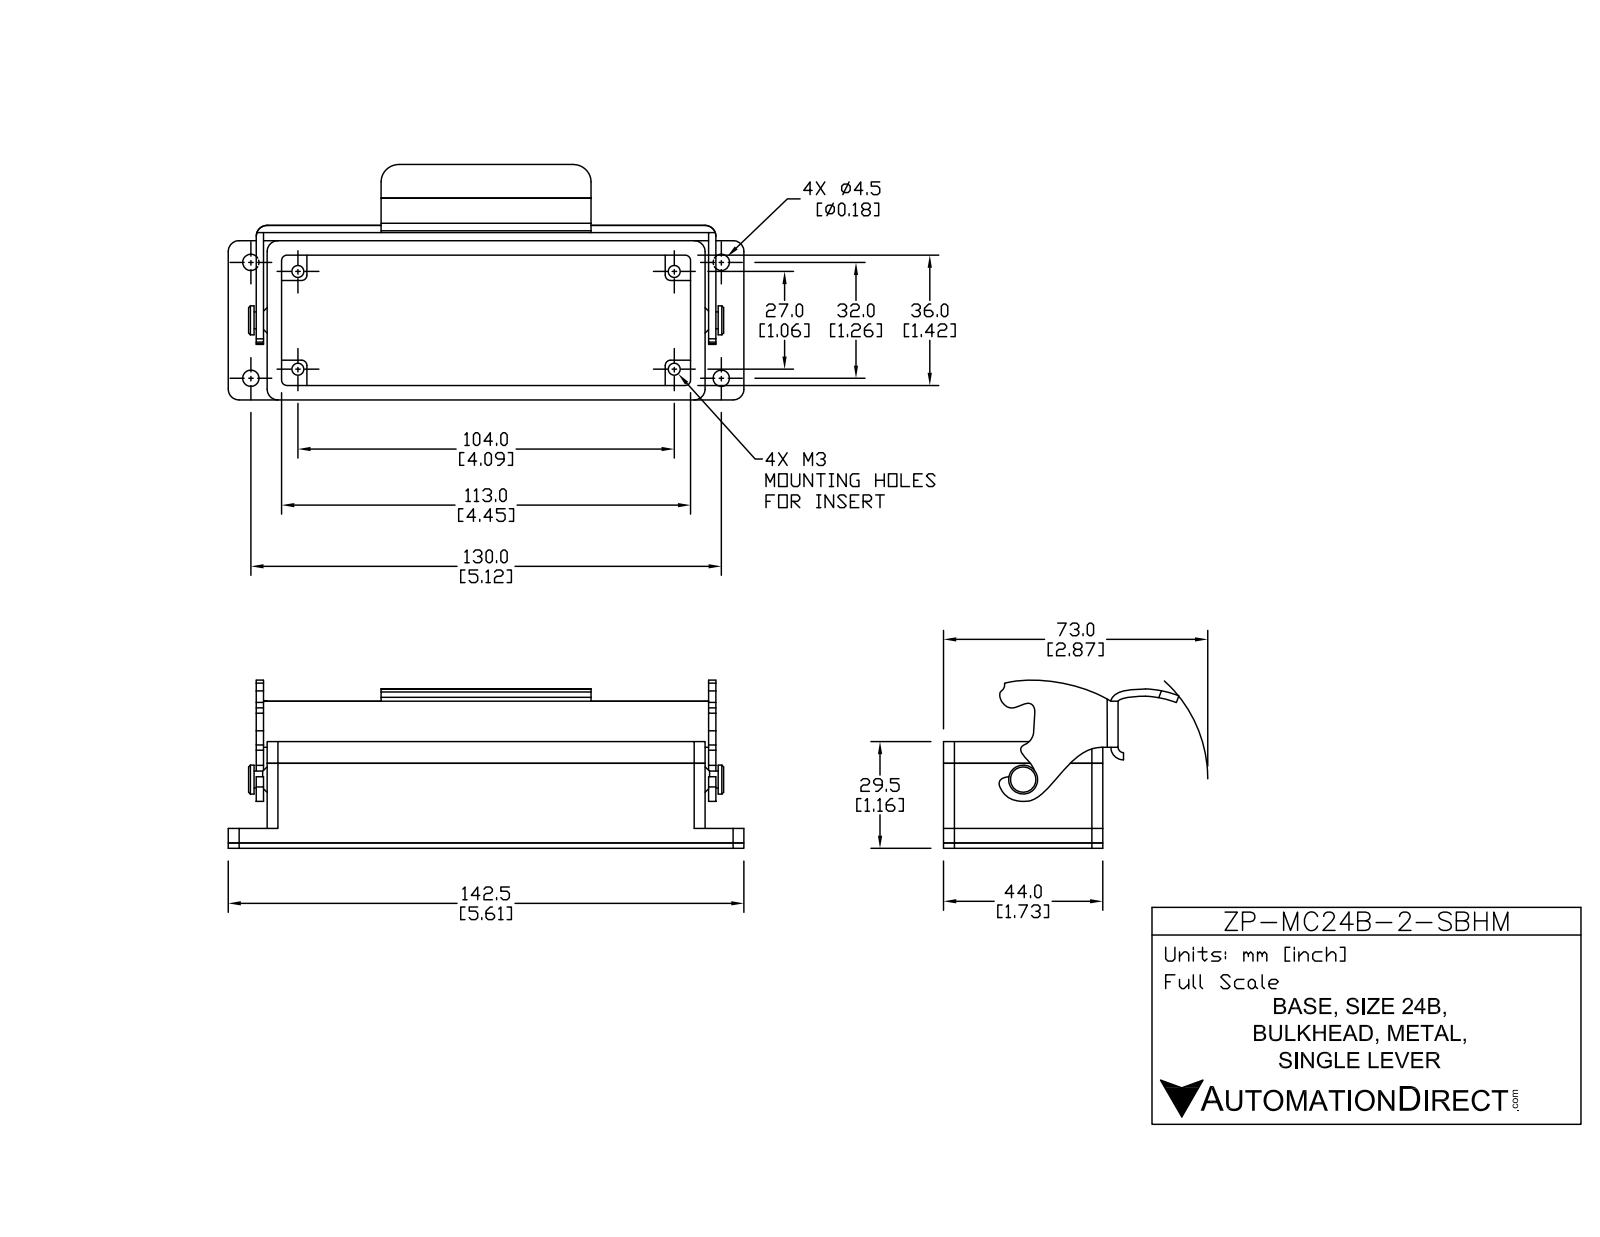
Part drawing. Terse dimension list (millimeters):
name: ZP-MC24B-2-SBHM
written by: SolidWorks 2011 (AUTOMOTIVE_DESIGN)
unit: mm
bodies: 4 solids, 208 faces (92 planar, 112 cylindrical, 4 other)
size: 142.5 × 69.95 × 44.44
volume: 42 967 mm³; area: 38 131 mm²
holes: 4× ⌀3.3, 4× ⌀4.5
bosses: 1× ⌀8, 1× ⌀4.67
rounds: 13× R0.5, 12× R1.5, 9× R3, 3× R2, 3× R4, 2× R1, 2× R10, 1× R0.92
face distances: 4, 3, 1, 44, 41, 40, 37, 22, 1.5, 23.5
hole spacings: 13.24, 32.24, 117.03, 120.66, 27, 32, 104, 107.45
